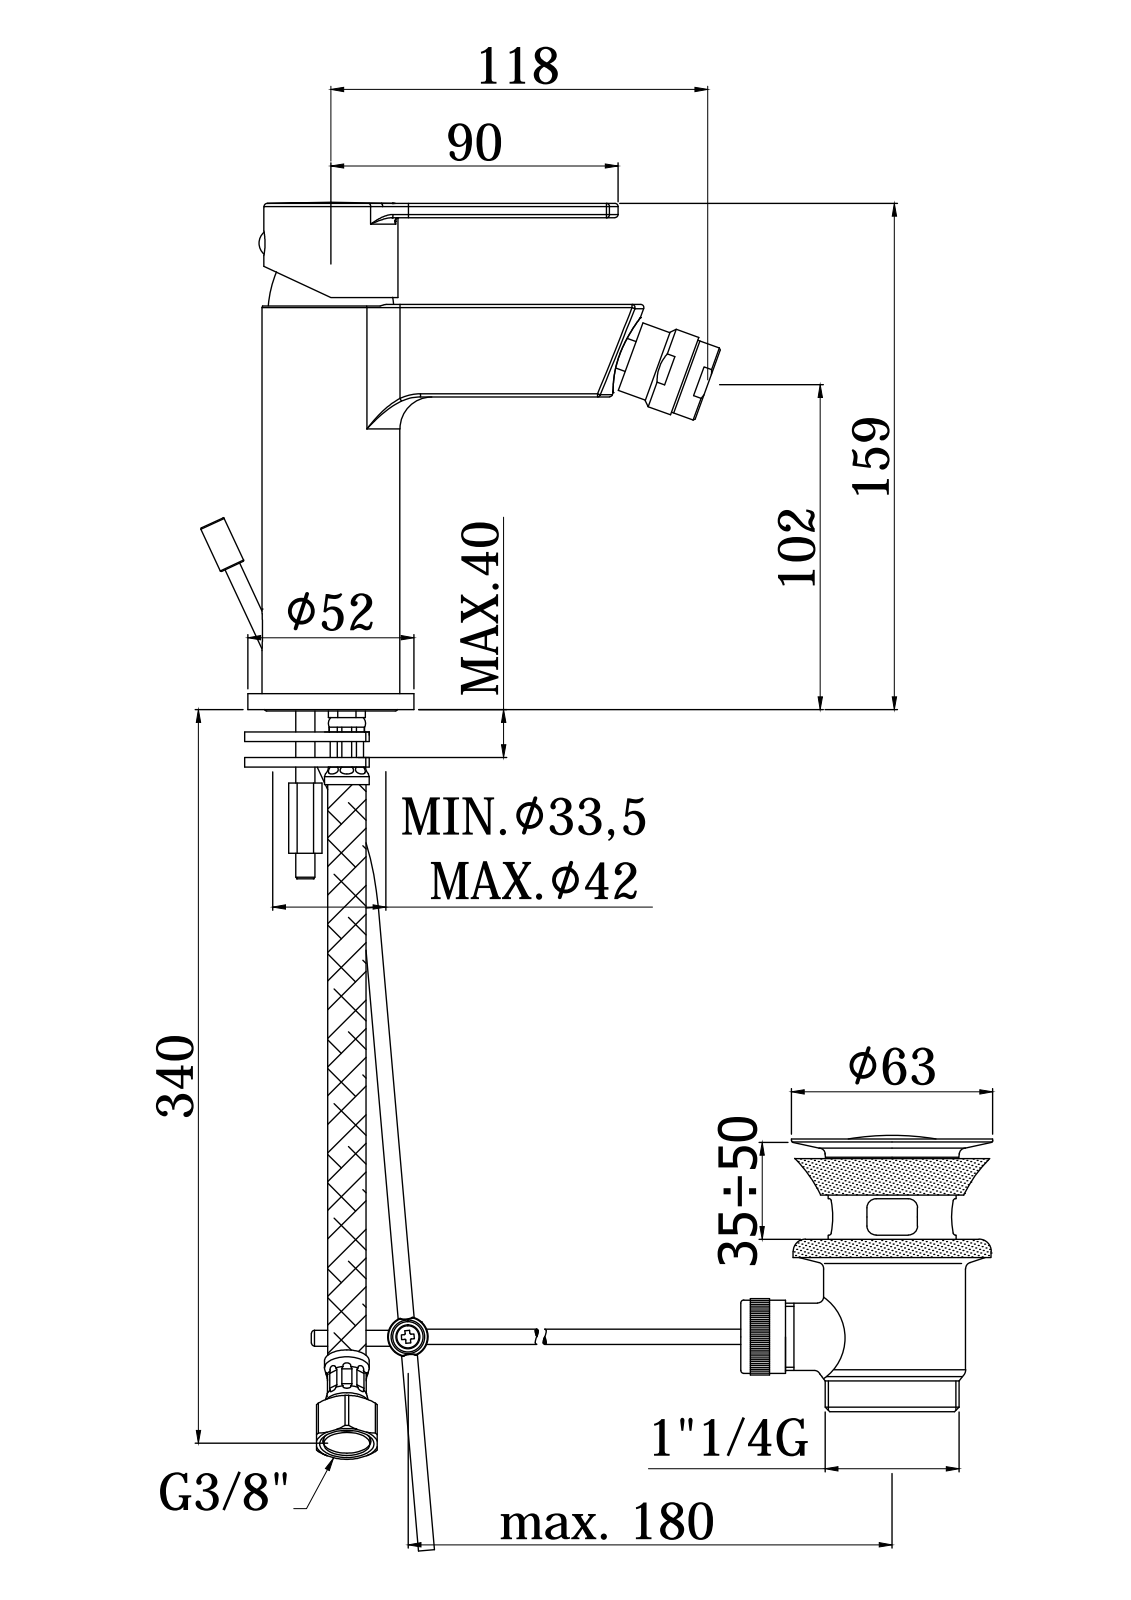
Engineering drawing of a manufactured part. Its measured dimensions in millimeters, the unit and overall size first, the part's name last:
Units: millimetres
Overall size (bounding box): 163.04 × 158.92 × 52
Round holes (diameter × count): ⌀5.5 ×5, ⌀8 ×3, ⌀7 ×2, ⌀9 ×2, ⌀11 ×2, ⌀16 ×2, ⌀3 ×1, ⌀3.4 ×1, ⌀3.5 ×1, ⌀4 ×1, ⌀4.6 ×1, ⌀7.8 ×1
Round bosses / shafts (diameter × count): ⌀4.8 ×2, ⌀4 ×2, ⌀52 ×1, ⌀43.2 ×1, ⌀42.6 ×1, ⌀42 ×1, ⌀37.8 ×1, ⌀36.8 ×1
Partial cylindrical surfaces — rounded edges, fillets, slot ends (radius × count): R0.5 ×54, R1 ×31, R1.5 ×29, R2 ×13, R1.7 ×6, R0.8 ×4, R5.8 ×4, R20 ×4
Main face-to-face distances: 3.5, 27.5, 25.5, 1, 31, 29, 3, 5, 123.5, 28.5
Hole centre spacings: 13.6, 0.5, 2.83, 8.6, 9.01, 13.45, 13.46, 14.5
Volume: 168 844 mm³ · Surface area: 104 197 mm²
Bodies: 4 solids, 3410 faces (2388 planar, 537 cylindrical, 485 other)
Part name (STEP PRODUCT): RIN135CR
STEP written by: CREO PARAMETRIC BY PTC INC, 2020044 (CONFIG_CONTROL_DESIGN)
